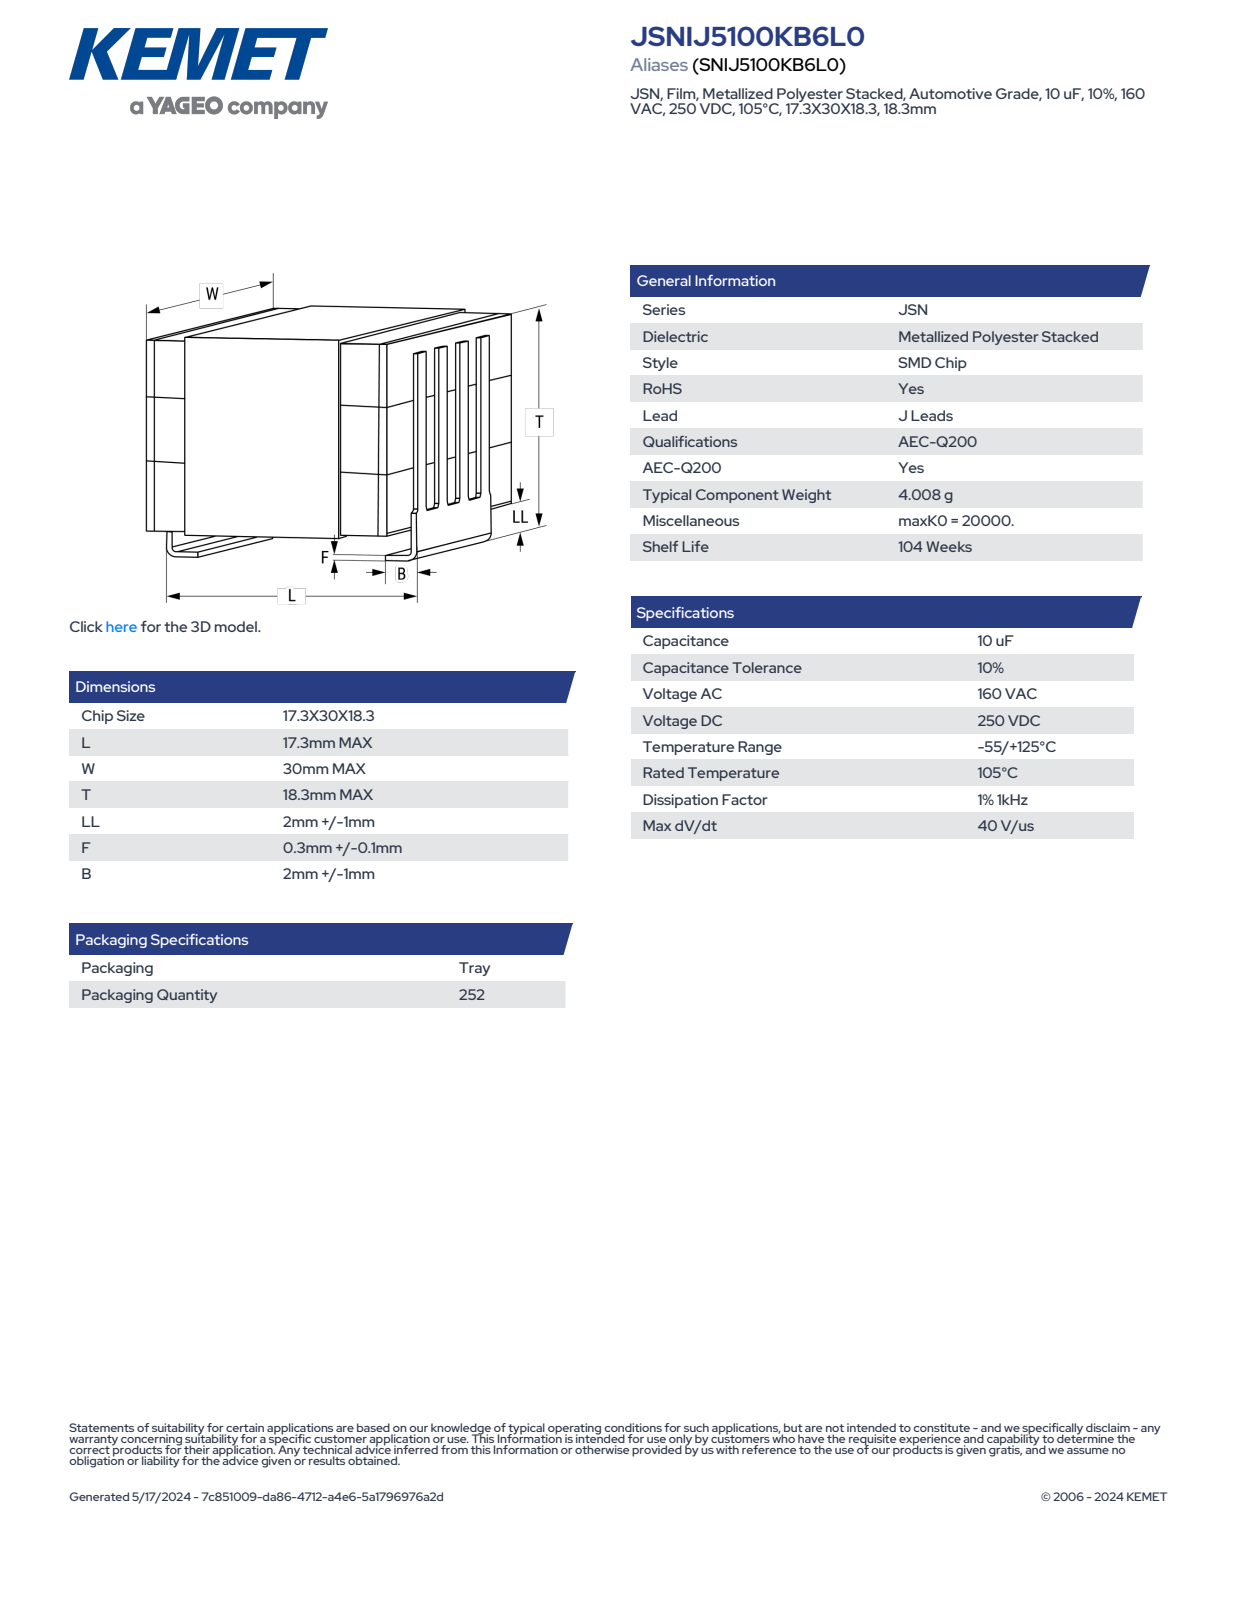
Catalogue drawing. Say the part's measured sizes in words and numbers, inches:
The part is named "CFS_KJSN_L17.3W30T18.3F0.40". Its 3-D file was written by "SolidWorks 2014 (AUTOMOTIVE_DESIGN)". It is 4 solids with 101 faces: 97 planar, 4 cylindrical and 0 other. Overall it measures 1.181 by 0.72 by 0.681 inches. Its volume is 0.47 cubic inches and its surface area 6.45 square inches. Partial cylindrical surfaces (rounded edges, fillets, slot ends): 4 of radius 0.008. The main face-to-face distances are 0.199, 0.4, 0.016, 0.195, 0.201, 0.396, 0.665, 0.203, 0.404, 0.598.
